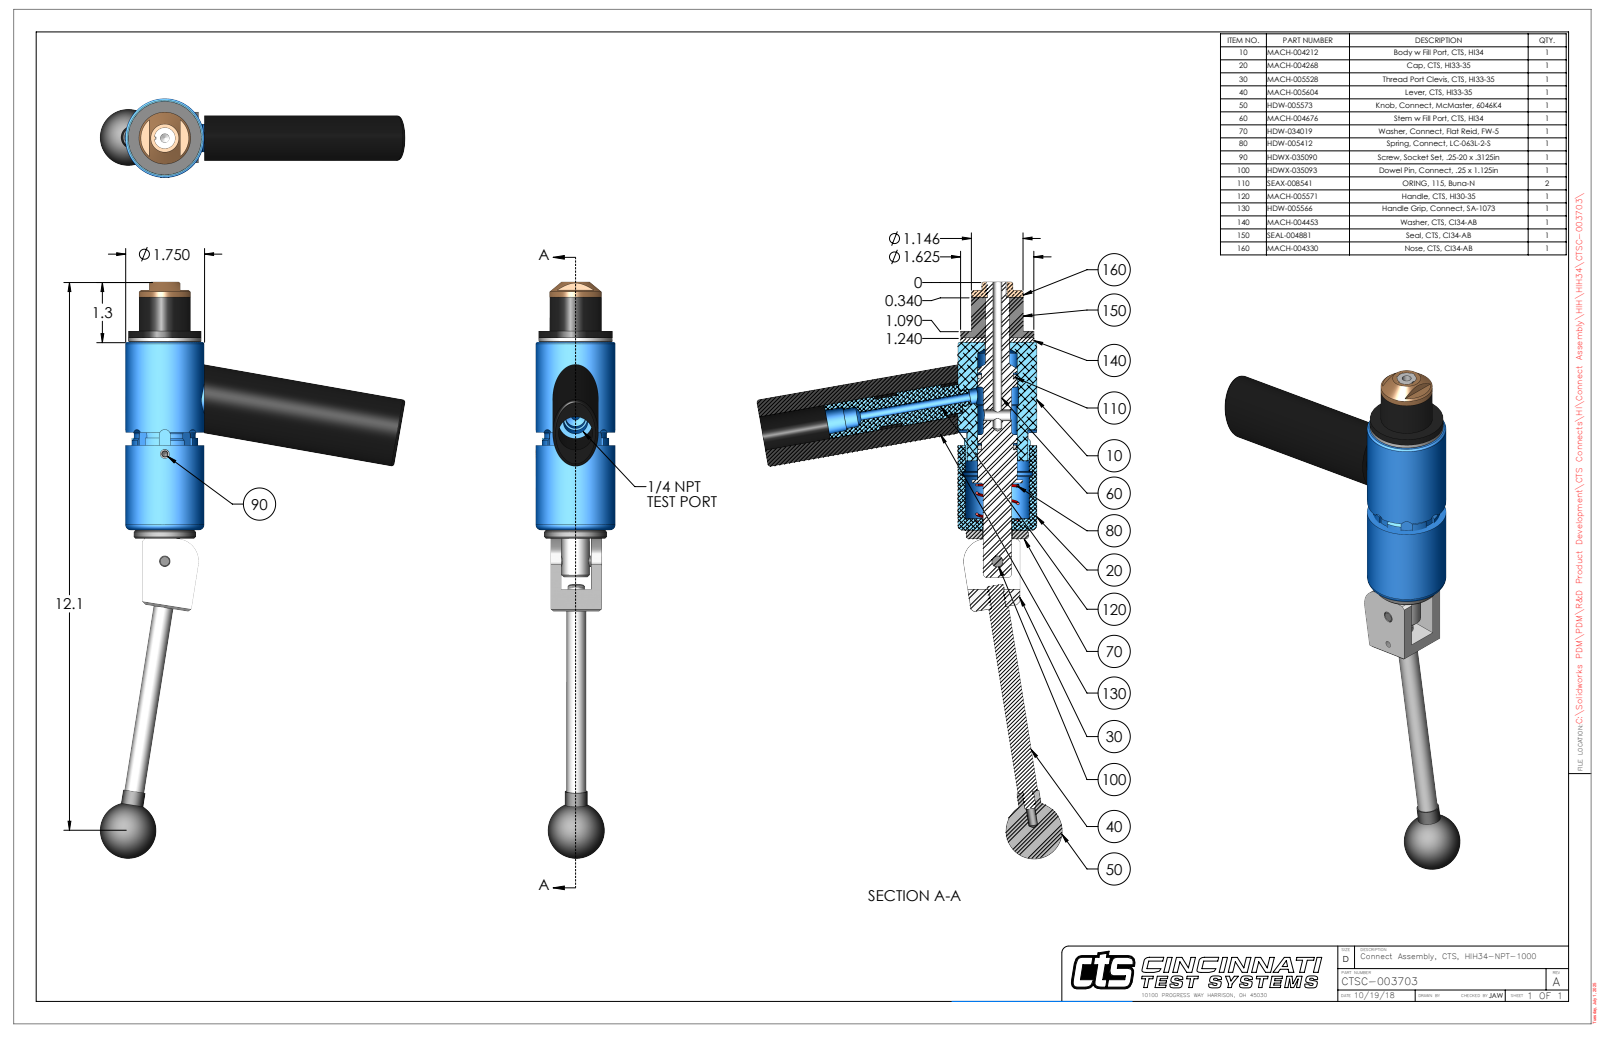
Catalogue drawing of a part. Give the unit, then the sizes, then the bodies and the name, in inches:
Units: inches
Overall size (bounding box): 12.773 × 6.763 × 1.75
Round holes (diameter × count): ⌀0.201 ×2, ⌀0.15 ×1, ⌀0.187 ×1, ⌀0.204 ×1, ⌀0.249 ×1, ⌀0.25 ×1, ⌀0.251 ×1, ⌀0.313 ×1, ⌀0.422 ×1, ⌀0.438 ×1, ⌀0.53 ×1, ⌀0.541 ×1
Round bosses / shafts (diameter × count): ⌀0.5 ×2, ⌀0.44 ×2, ⌀0.25 ×2, ⌀1.75 ×1, ⌀1.625 ×1, ⌀1.38 ×1, ⌀1.146 ×1, ⌀0.75 ×1
Partial cylindrical surfaces — rounded edges, fillets, slot ends (radius × count): R0.125 ×4, R0.029 ×2, R0.166 ×1, R0.166 ×1, R0.181 ×1, R0.33 ×1, R0.5 ×1, R0.695 ×1
Main face-to-face distances: 0.094, 4.258, 4.164, 0.9, 0.994, 5.158, 1.12, 5.346, 4.446, 4.352
Hole centre spacings: 0.74, 2.376, 3.116
Volume: 18.8 in³ · Surface area: 119.5 in²
Bodies: 10 solids, 329 faces (117 planar, 142 cylindrical, 70 other)
Part name (STEP PRODUCT): CTSC-003703
STEP written by: SolidWorks 2023 (AUTOMOTIVE_DESIGN)
